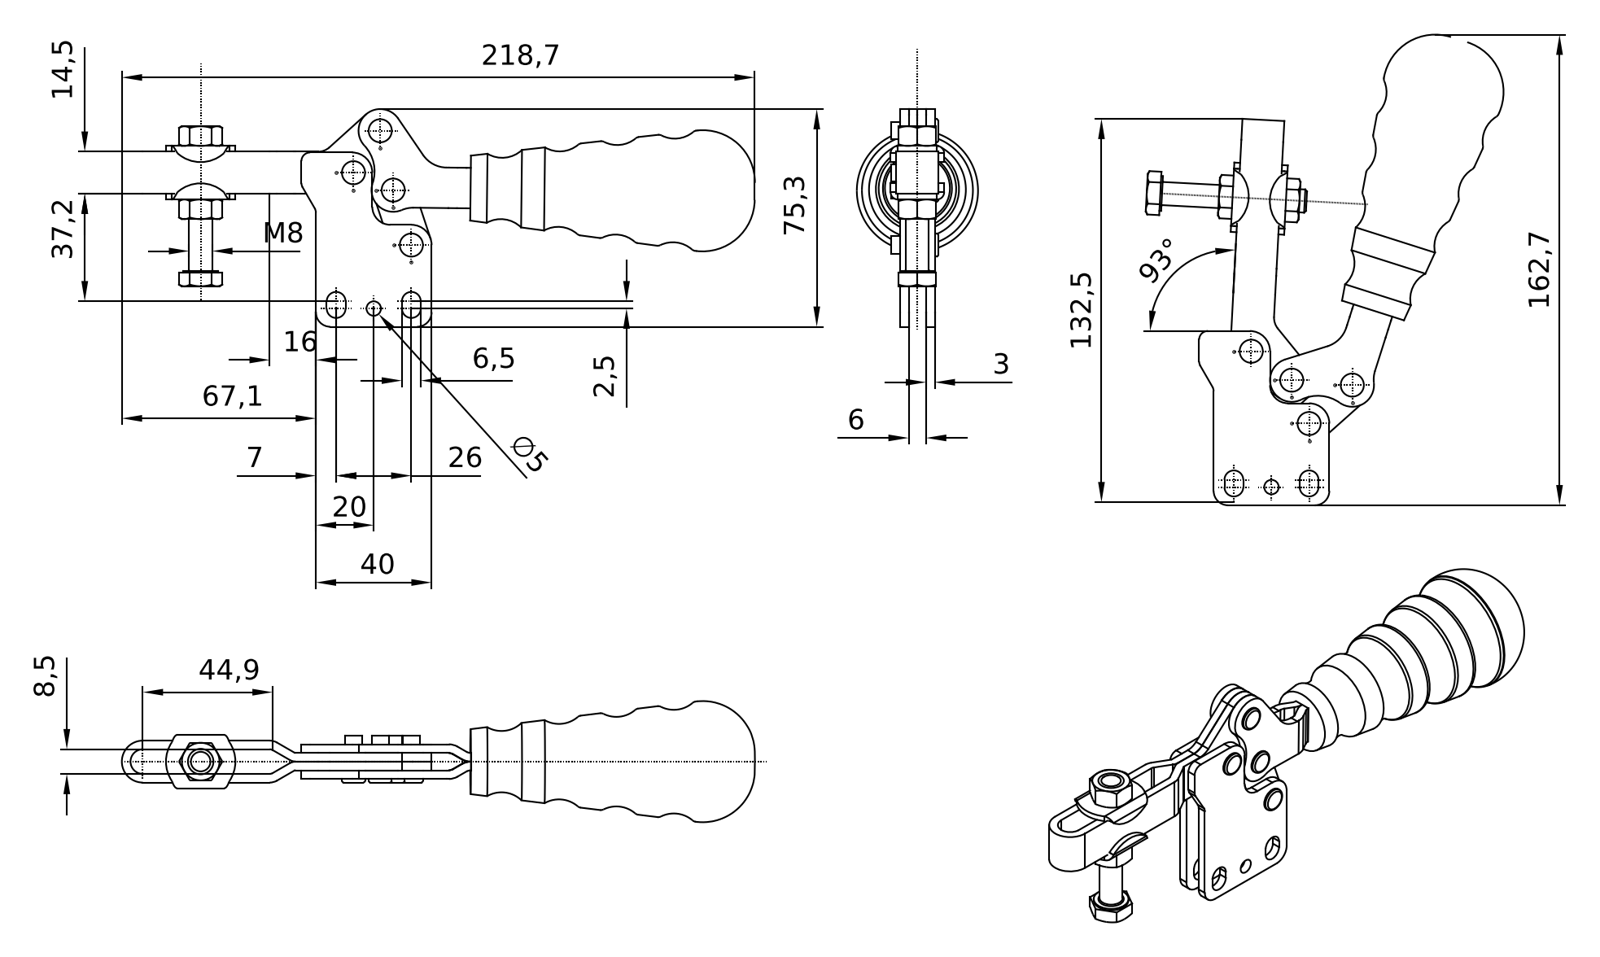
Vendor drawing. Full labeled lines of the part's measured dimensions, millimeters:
STEP written by: Autodesk Inventor 8 (AUTOMOTIVE_DESIGN)
Units: millimetres
Bodies: 1 solid, 1078 faces (407 planar, 213 cylindrical, 458 other)
Overall size (bounding box): 218.82 × 75.26 × 41.89
Volume: 112 740 mm³ · Surface area: 35 757 mm²
Round holes (diameter × count): ⌀6.04 ×4, ⌀5 ×1, ⌀9 ×1
Round bosses / shafts (diameter × count): ⌀8 ×5, ⌀6 ×4, ⌀12 ×1
Partial cylindrical surfaces — rounded edges, fillets, slot ends (radius × count): R3 ×5, R2.5 ×4, R3.25 ×4, R6 ×4, R7 ×4, R5 ×3, R12 ×3, R0.5 ×2
Main face-to-face distances: 3, 9.02, 6.02, 12.02, 1.24, 10.26, 4.24, 10.22, 8.98, 5.98
Hole centre spacings: 14.98, 17.2, 20.01, 21, 25.51, 32.02, 40.95, 41.5
